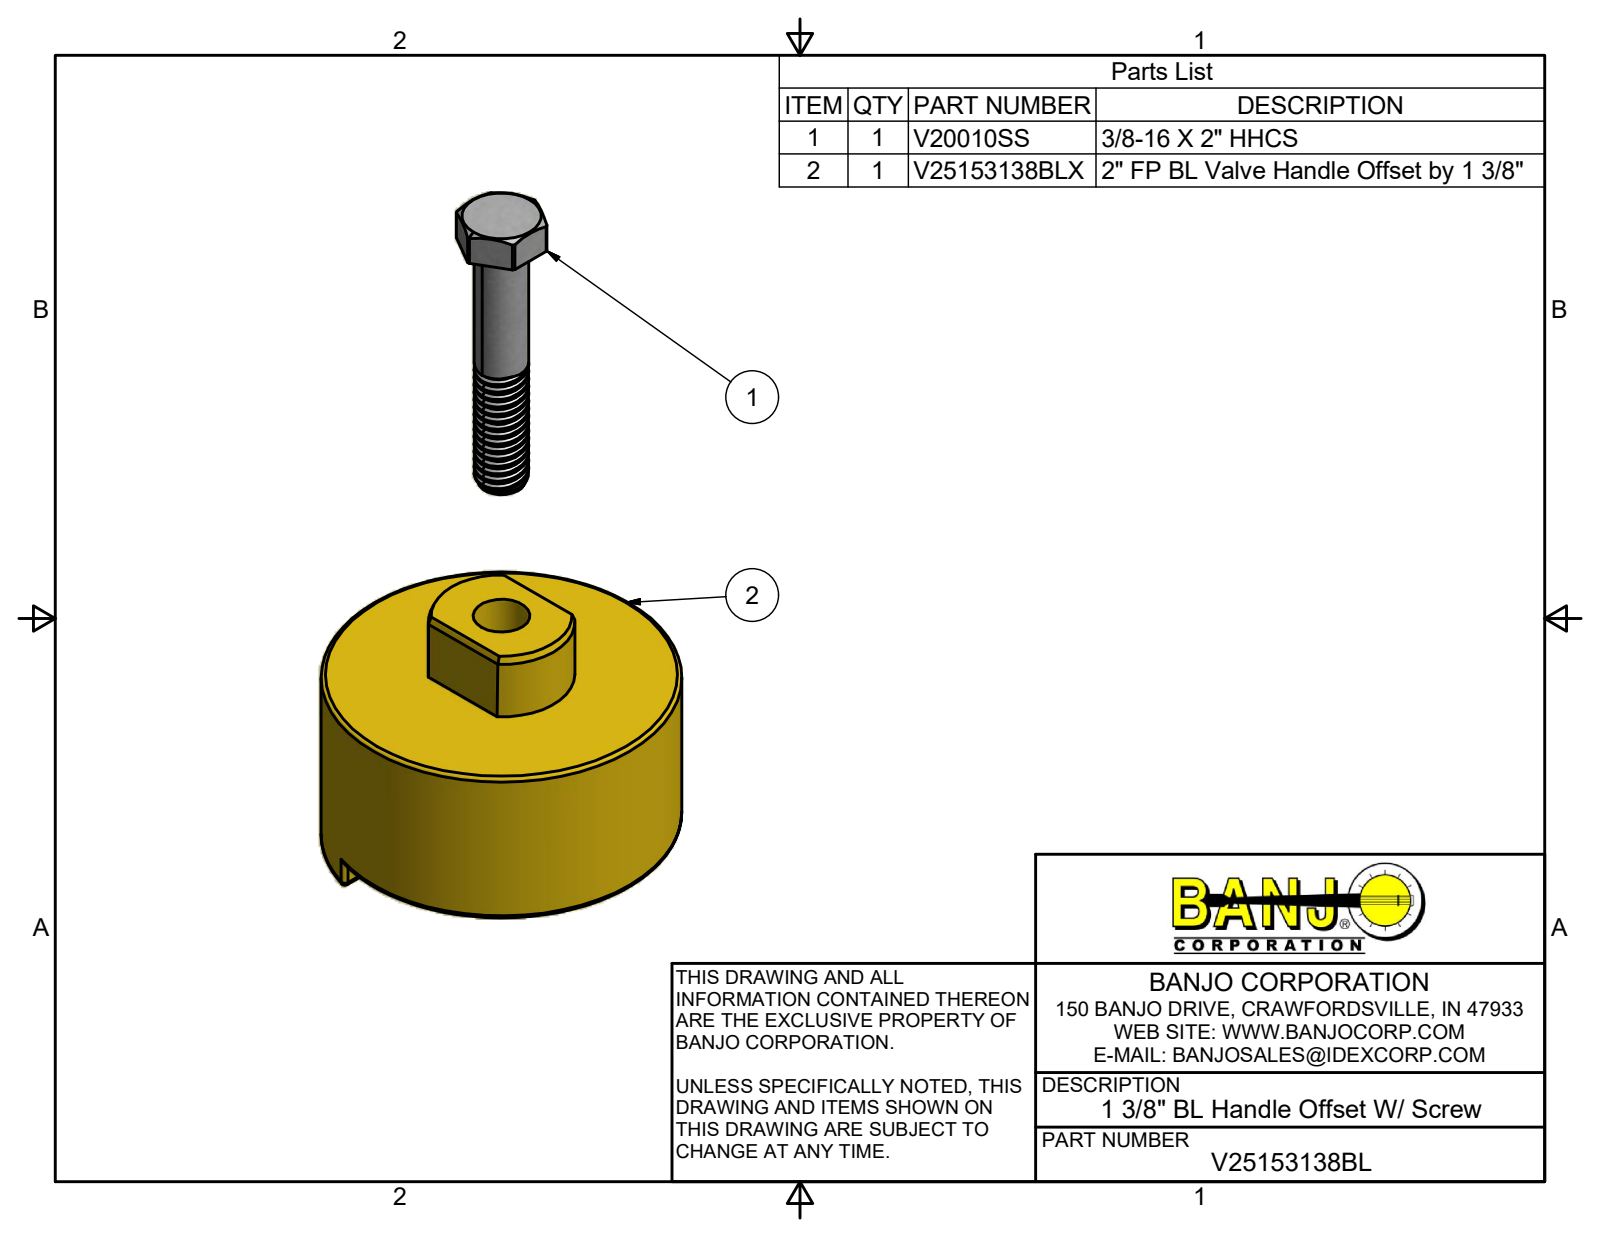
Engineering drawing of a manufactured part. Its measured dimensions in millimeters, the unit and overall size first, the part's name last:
Units: millimetres
Overall size (bounding box): 132.95 × 62.99 × 62.99
Round holes (diameter × count): ⌀9.91 ×1, ⌀56.64 ×1
Round bosses / shafts (diameter × count): ⌀8.24 ×15, ⌀62.99 ×1, ⌀39.12 ×1, ⌀9.52 ×1
Partial cylindrical surfaces — rounded edges, fillets, slot ends (radius × count): R0.76 ×5, R1.52 ×4, R4.12 ×2, R8.12 ×1, R12.8 ×1
Main face-to-face distances: 3.17, 31.75, 34.92, 7.62, 6.42, 12.76, 12.83, 18.92, 22.09, 4.83
Volume: 73 537 mm³ · Surface area: 26 795 mm²
Bodies: 2 solids, 211 faces (33 planar, 93 cylindrical, 85 other)
Part name (STEP PRODUCT): V25153138BL; V25153138BLX; V20010SS
STEP written by: Autodesk Inventor 2017 (AUTOMOTIVE_DESIGN)
